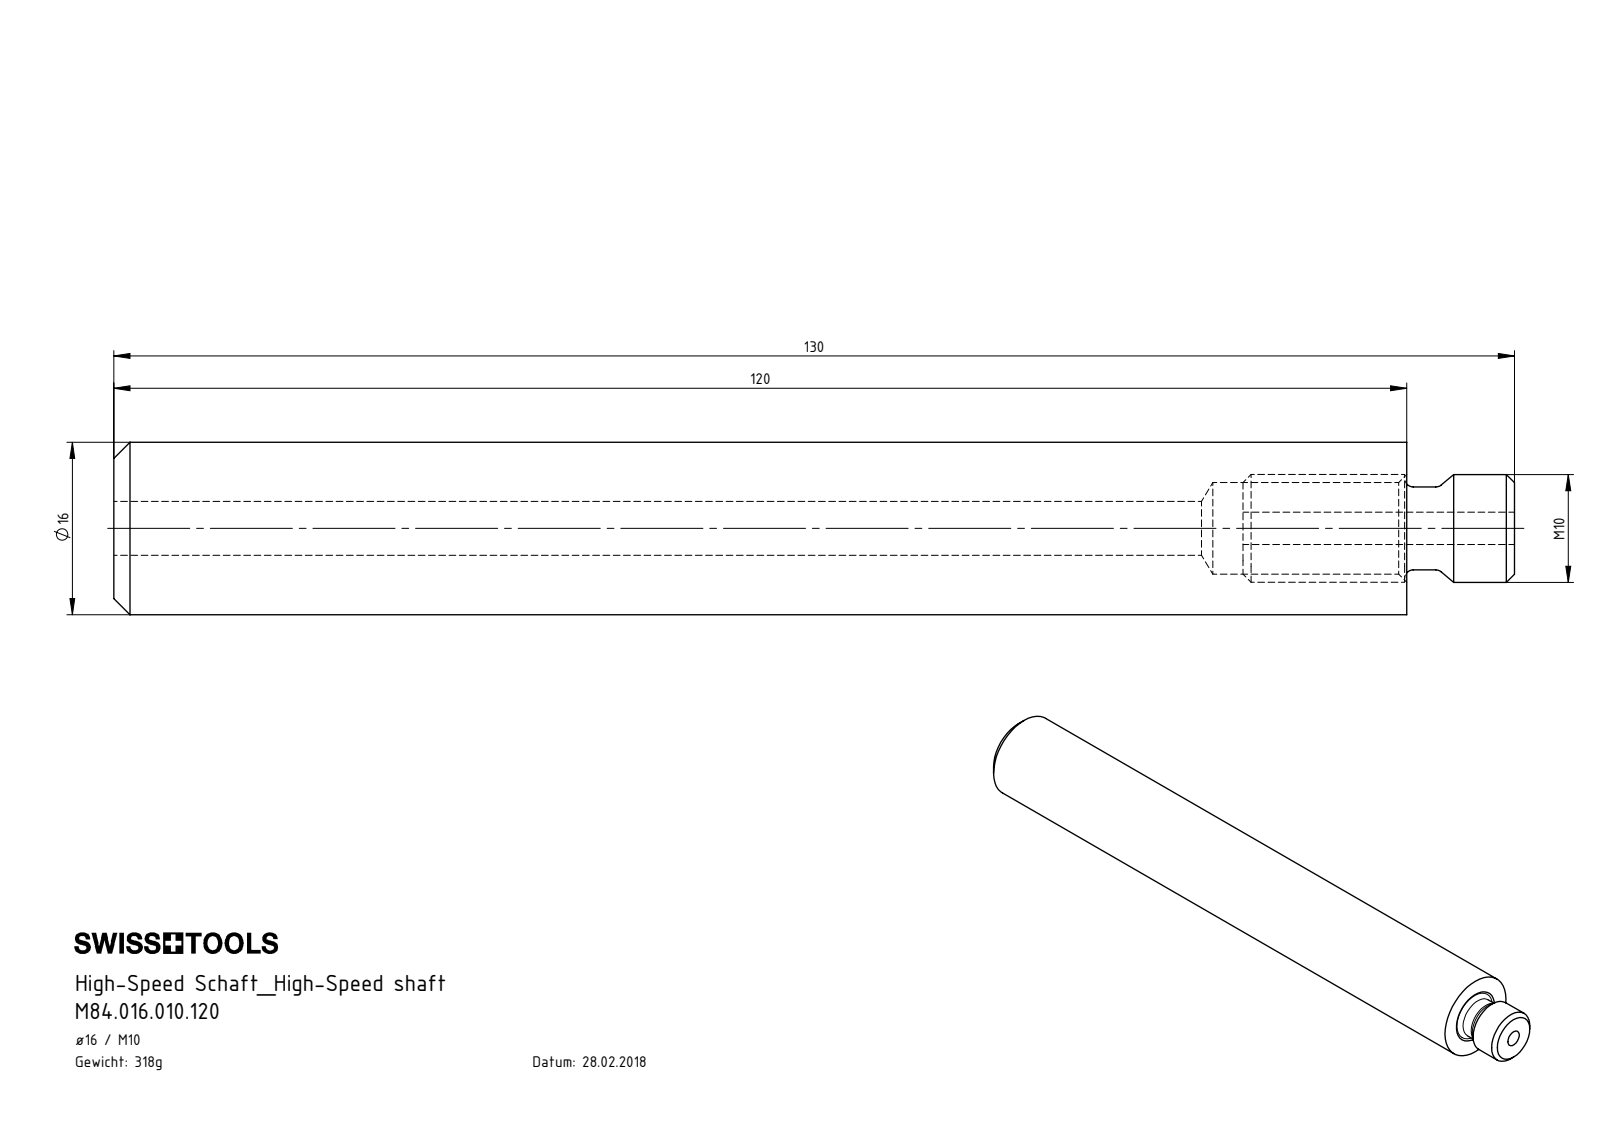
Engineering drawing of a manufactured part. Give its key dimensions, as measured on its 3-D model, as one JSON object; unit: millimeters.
{"part_name": "U16.HS0.K01.120; HM1-U16.001.120_A; HM1-BG1.010.025_A", "step_written_by": "SolidWorks 2017 (AUTOMOTIVE_DESIGN)", "units": "millimeters", "bodies": {"solids": 2, "faces": 20, "planar": 5, "cylindrical": 7, "other": 8}, "overall_size": [130, 16, 16], "volume_mm3": 22687, "surface_area_mm2": 9559, "round_holes": [[3, 1], [5, 1], [8.5, 1]], "round_bosses_or_shafts": [[16, 1], [10, 1], [7.7, 1]], "face_to_face_distances": [120, 104.8, 130, 15.2, 25.2, 10, 119.8, 15, 10.2]}
